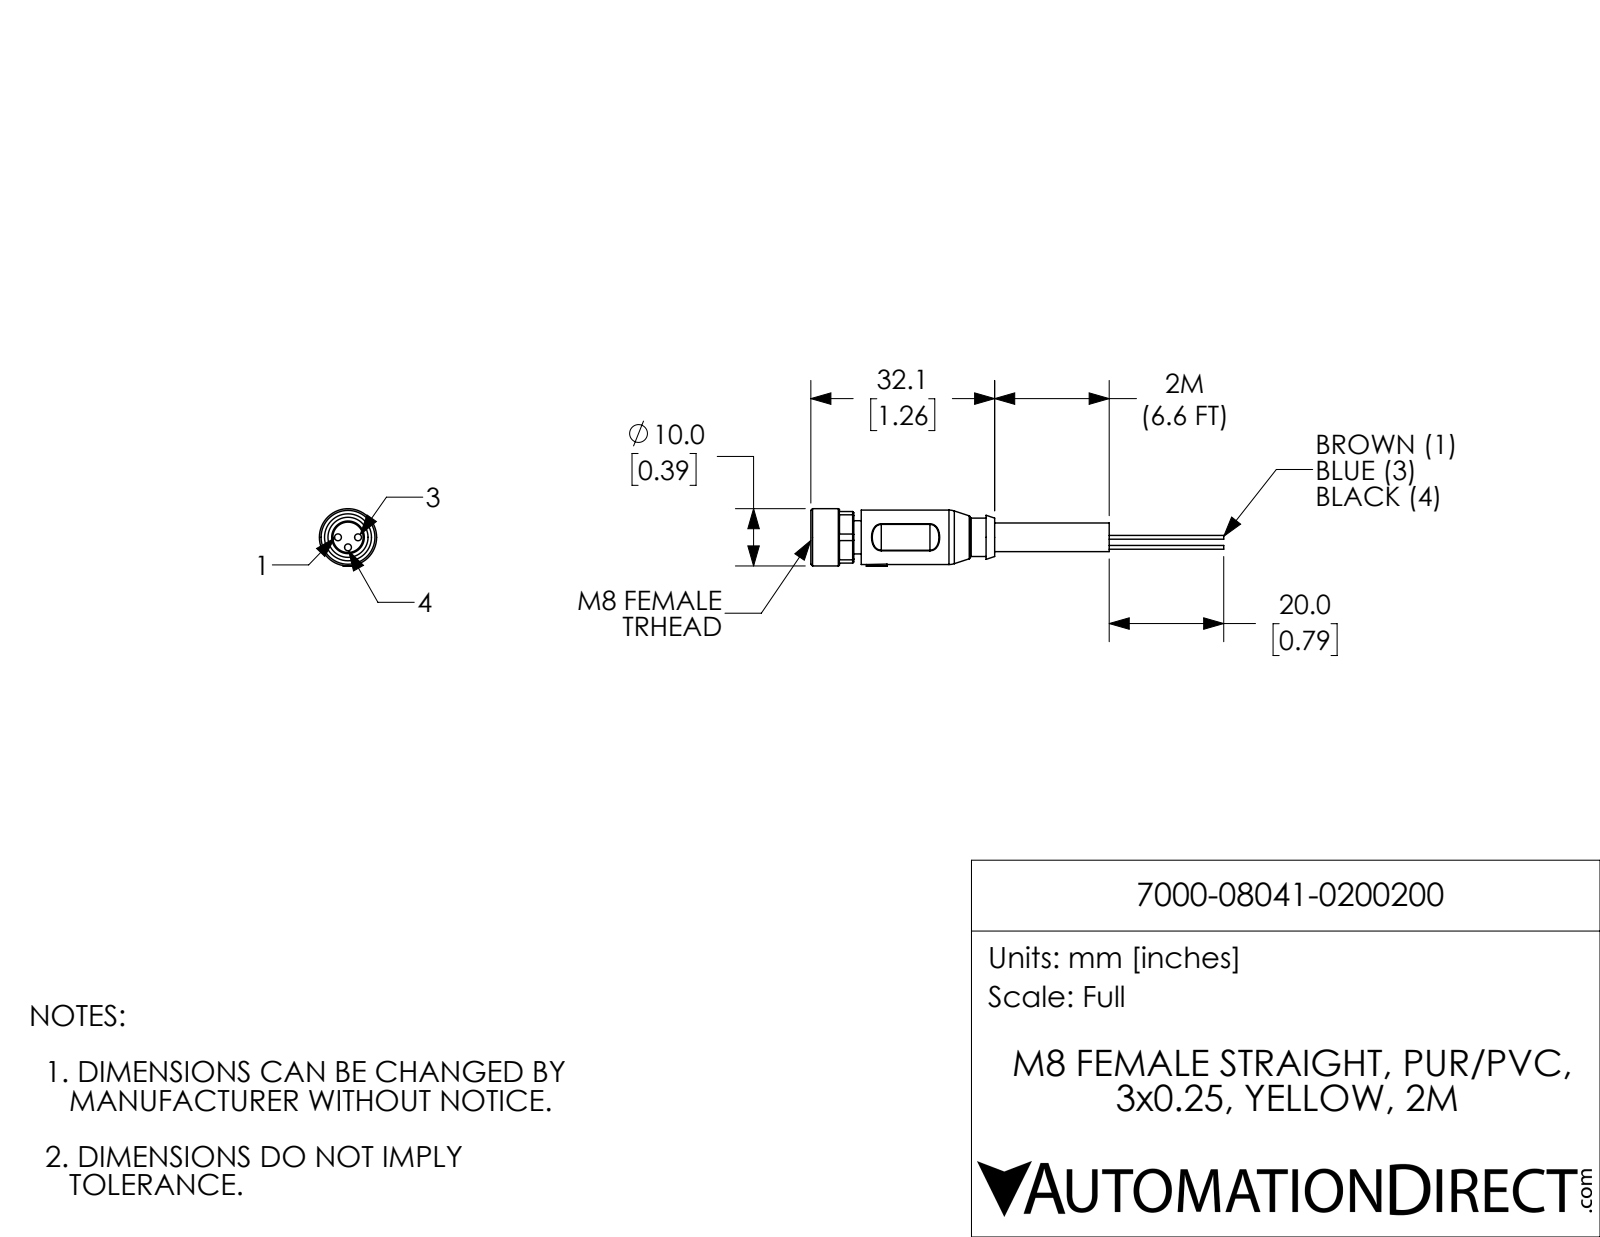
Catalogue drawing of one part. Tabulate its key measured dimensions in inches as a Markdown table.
| quantity | value |
| --- | --- |
| part name | 7000-08041-0200200 |
| STEP written by | SolidWorks 2017 (AUTOMOTIVE_DESIGN) |
| units | inches |
| bodies | 1 solid, 109 faces (36 planar, 42 cylindrical, 31 other) |
| overall size | 2.839 × 0.396 × 0.394 |
| volume | 0.141 in³ |
| surface area | 2.851 in² |
| round holes (diameter × count) | 0.047 × 3, 0.276 × 1 |
| round bosses / shafts (diameter × count) | 0.026 × 3, 0.394 × 1, 0.374 × 1, 0.264 × 1, 0.228 × 1, 0.224 × 1, 0.197 × 1 |
| partial cylindrical surfaces (radius × count) | 0.008 × 4, 0.098 × 4, 0.193 × 1, 0.199 × 1 |
| main face-to-face distances | 0.327, 0.051, 0.969, 0.354, 0.059, 0.028, 0.268, 0.319, 2.024, 1.756 |
| hole center spacings | 0.069, 0.097, 0.138 |
